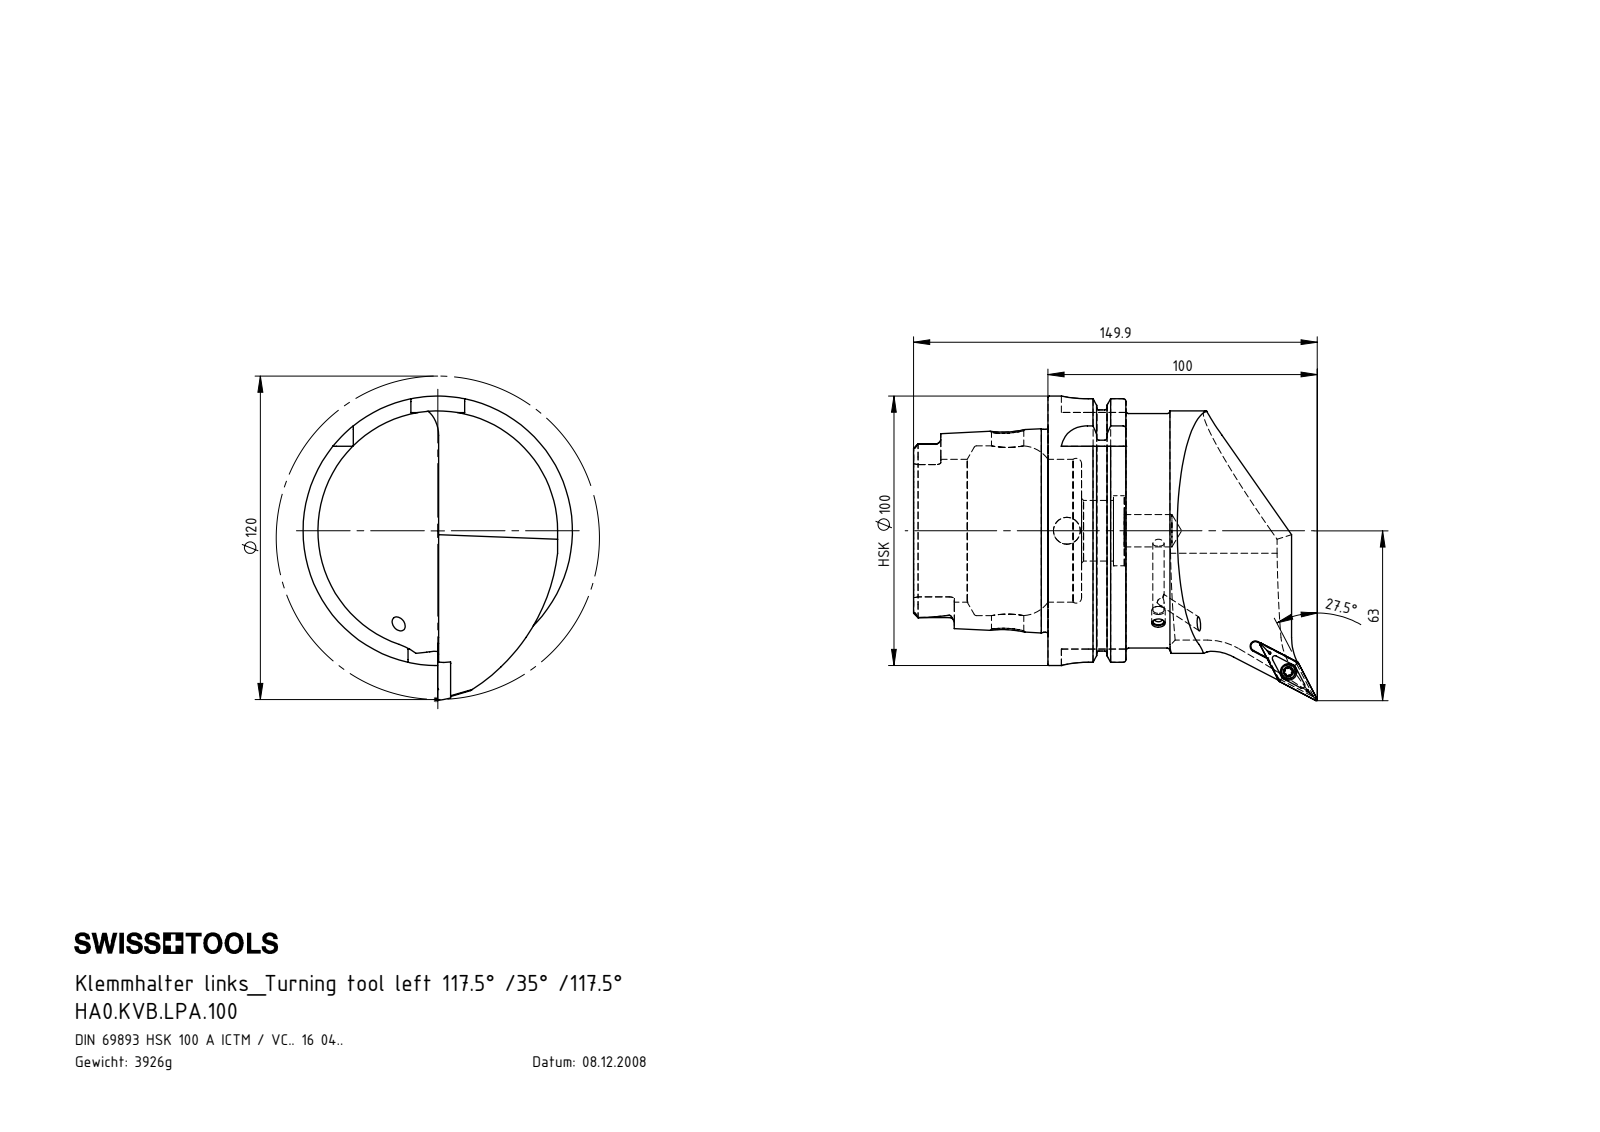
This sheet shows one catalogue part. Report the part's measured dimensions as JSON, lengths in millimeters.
{"part_name": "KVT_MB_600_050; WCB-ER2.001.009_A; HA0-KVB.LPA.100_A_Fertigbearbeitung; VCMT160404 (+1 more)", "step_written_by": "SolidWorks 2009 (CONFIG_CONTROL_DESIGN)", "units": "millimeters", "bodies": {"solids": 5, "faces": 314, "planar": 79, "cylindrical": 89, "other": 146}, "overall_size": [149.92, 113.02, 100], "volume_mm3": 499694, "surface_area_mm2": 66076, "round_holes": [[4.2, 2], [12, 2], [3.3, 1], [4, 1], [4.4, 1], [6.1, 1], [10, 1], [22.5, 1], [26, 1], [53, 1], [63, 1]], "round_bosses_or_shafts": [[100, 1], [91.95, 1], [87, 1], [75.26, 1], [5.25, 1], [5, 1], [4, 1]], "partial_cylinders_radius": [[0.34, 6], [0.59, 6], [1.9, 6], [10, 4], [4.83, 2], [4.88, 2], [1.75, 1], [6, 1]], "face_to_face_distances": [12.45, 28.95, 16.5, 49.9, 62.35, 78.85, 87.8, 78.2, 28.3, 15.85], "hole_center_spacings": [97.46, 97.57]}
